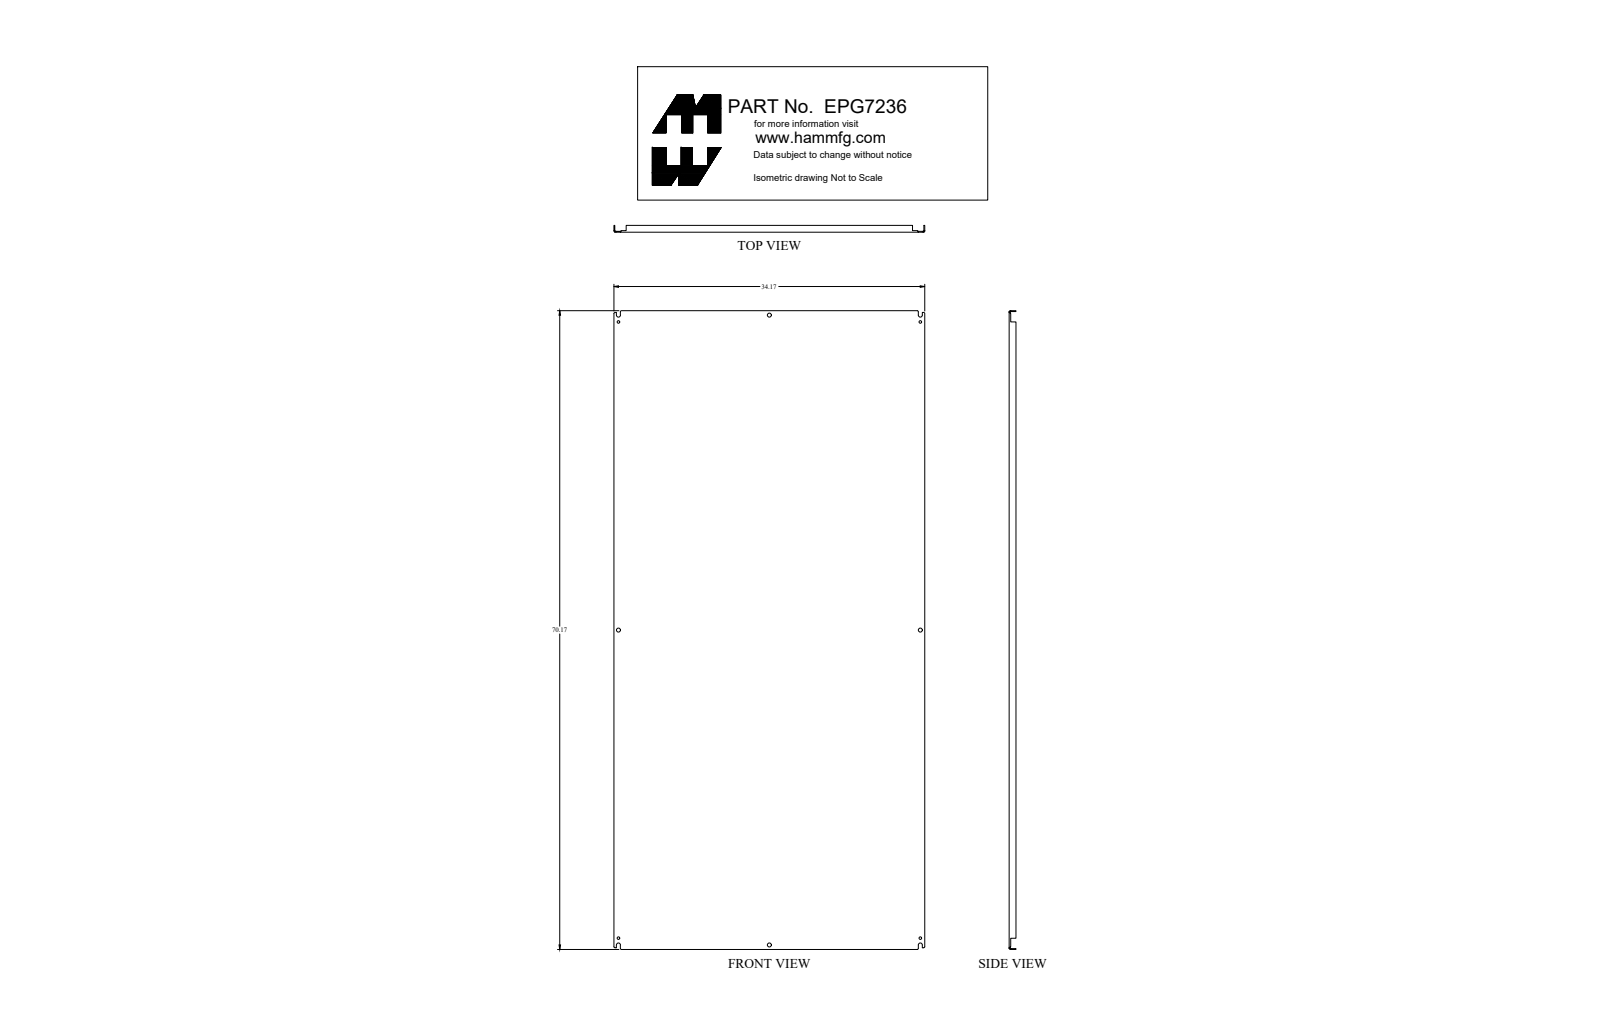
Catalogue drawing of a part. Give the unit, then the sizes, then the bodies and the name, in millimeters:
Units: millimetres
Overall size (bounding box): 1782.3 × 867.9 × 19.1
Round holes (diameter × count): ⌀7.1 ×4, ⌀11.1 ×4
Partial cylindrical surfaces — rounded edges, fillets, slot ends (radius × count): R1.2 ×4, R1.6 ×4, R3.6 ×4, R5.6 ×4
Main face-to-face distances: 2.4, 865.5, 867.9, 863.1, 1779.9, 1777.5, 1782.3, 19.1, 16.6, 4.3
Hole centre spacings: 421.9, 859.6, 974.5, 1204, 1788.7, 843, 1719.3, 1914.8
Volume: 3 918 000 mm³ · Surface area: 3 262 000 mm²
Bodies: 1 solid, 136 faces (74 planar, 46 cylindrical, 16 other)
Part name (STEP PRODUCT): EPG7236
STEP written by: SolidWorks 2018 (AUTOMOTIVE_DESIGN)
